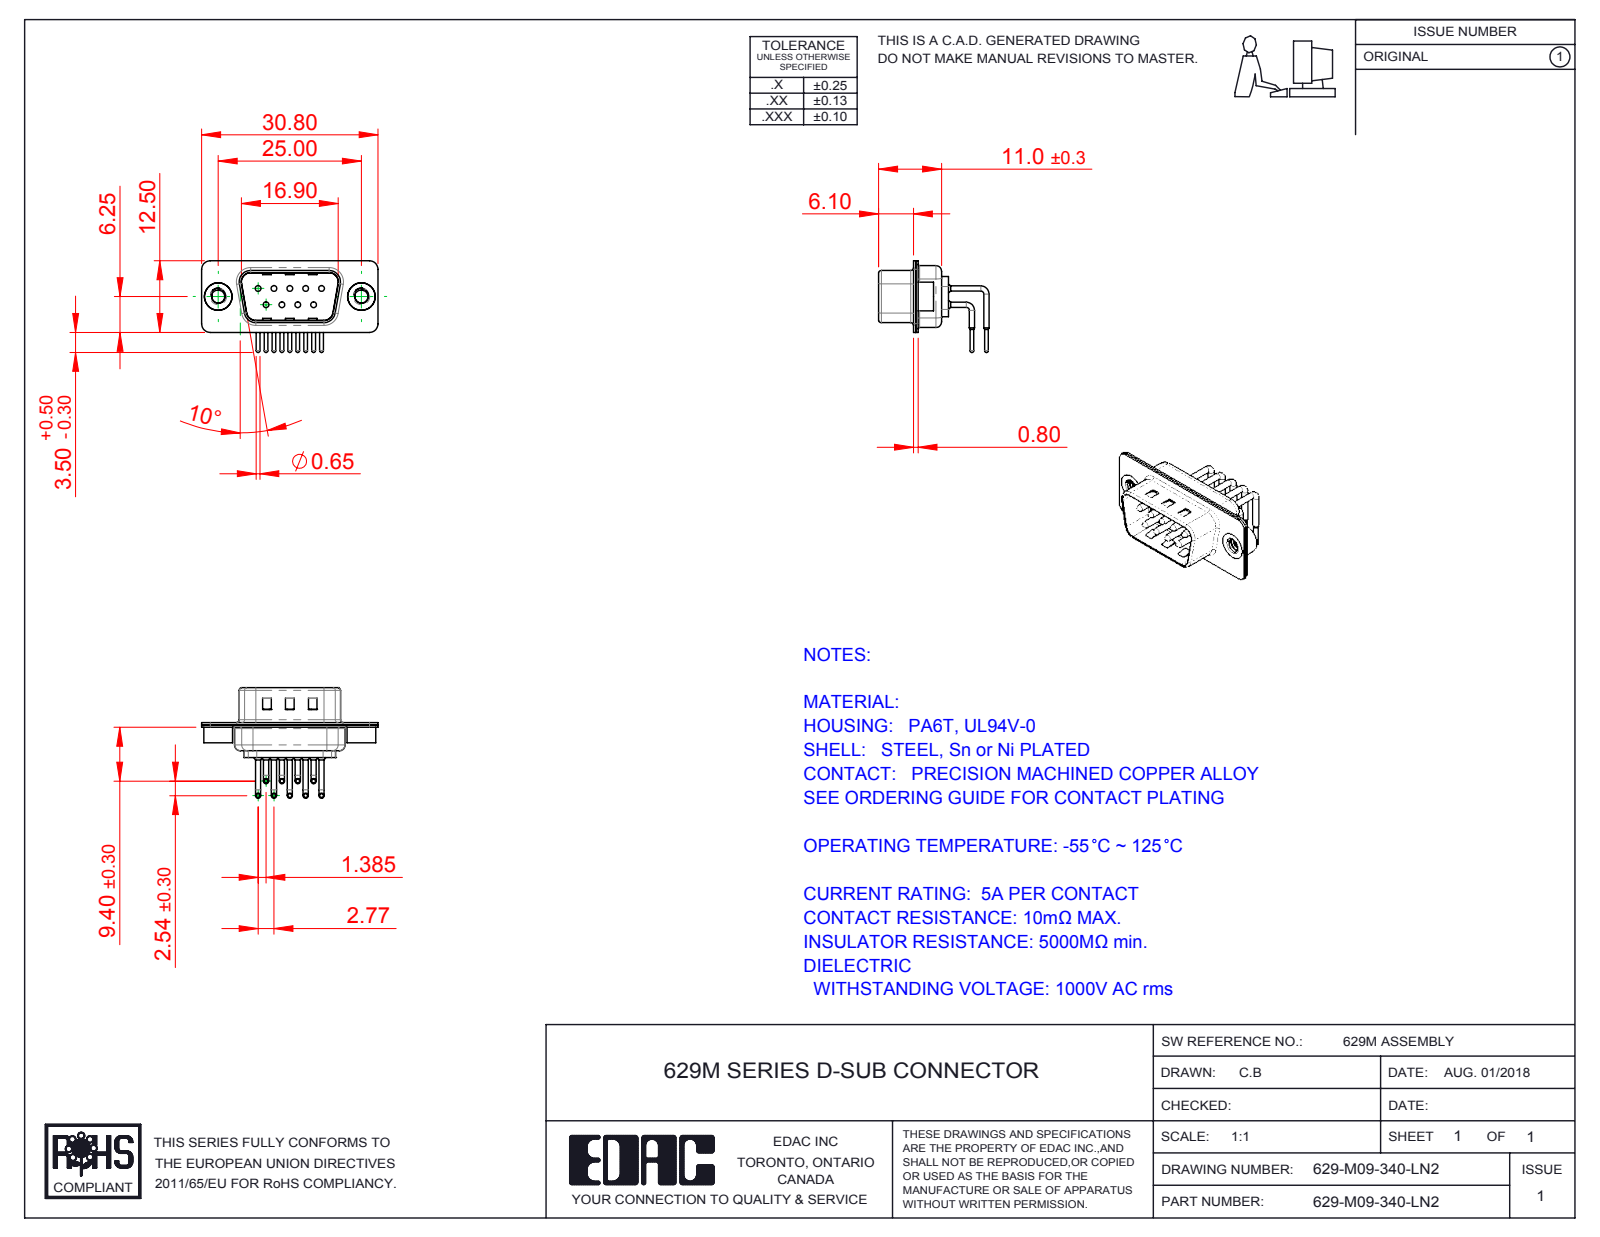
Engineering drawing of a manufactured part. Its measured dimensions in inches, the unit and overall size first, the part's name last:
Units: inches
Overall size (bounding box): 1.213 × 0.759 × 0.63
Round holes (diameter × count): ⌀0.039 ×9, ⌀0.067 ×9, ⌀0.079 ×9, ⌀0.089 ×2, ⌀0.157 ×2, ⌀0.189 ×2
Round bosses / shafts (diameter × count): ⌀0.035 ×18, ⌀0.059 ×9, ⌀0.026 ×9, ⌀0.197 ×2, ⌀0.193 ×2
Partial cylindrical surfaces — rounded edges, fillets, slot ends (radius × count): R0.059 ×16, R0.079 ×12, R0.04 ×9, R0.02 ×8, R0.063 ×8, R0.01 ×4, R0.024 ×4, R0.026 ×4
Main face-to-face distances: 0.016, 0.033, 0.031, 0.376, 0.049, 0.409, 0.343, 0.014, 0.24, 0.224
Hole centre spacings: 0.124, 0.109, 0.218, 0.198, 0.198, 0.327, 0.28, 0.294
Volume: 0.084 in³ · Surface area: 6.064 in²
Bodies: 14 solids, 1294 faces (683 planar, 453 cylindrical, 158 other)
Part name (STEP PRODUCT): 629M Shell Front_09 Contacts; 629M Contact Row 2; 629M Housing_09 Contacts; 629M Contact Row 1 (+3 more)
STEP written by: SolidWorks 2016 (CONFIG_CONTROL_DESIGN)
